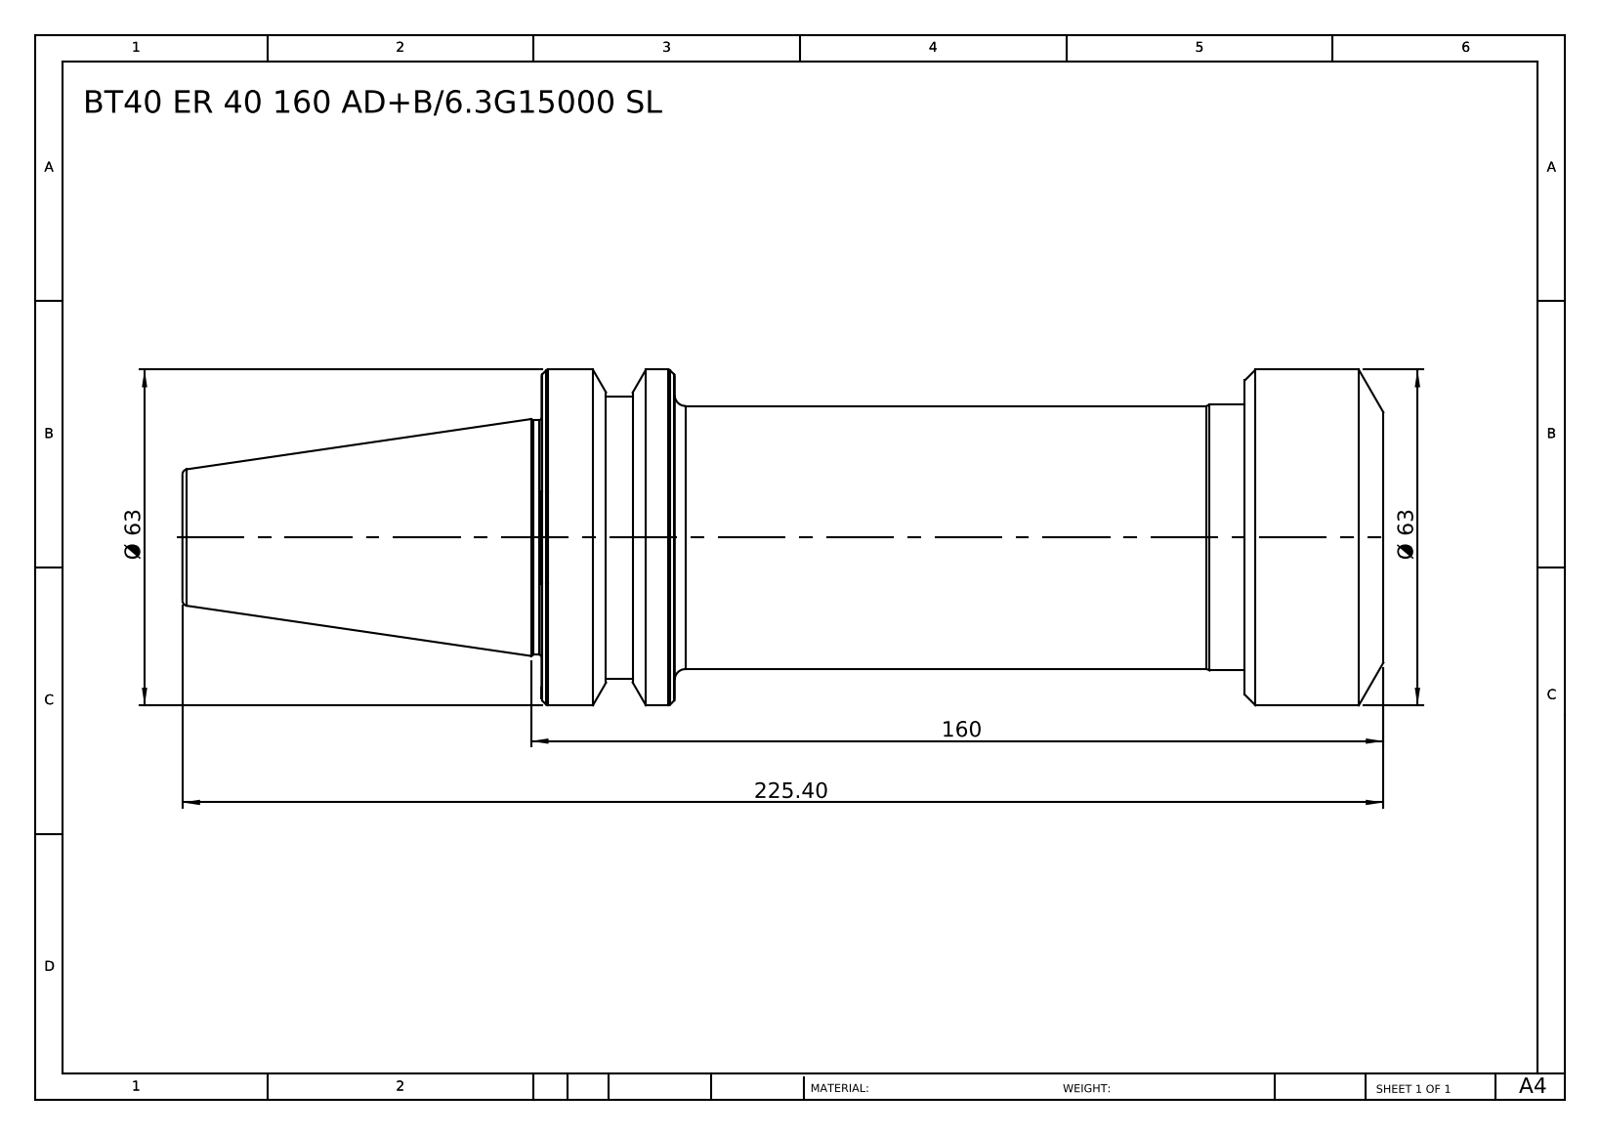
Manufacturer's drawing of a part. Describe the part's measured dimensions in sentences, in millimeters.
The part is named "BT40 ER 40 160 AD-6.3G15000 SL". Its 3-D file was written by "SolidWorks 2014 (CONFIG_CONTROL_DESIGN)". It is 1 solid with 62 faces: 7 planar, 14 cylindrical and 41 other. Overall it measures 225.4 by 63 by 63 millimeters. Its volume is 421 200 cubic millimeters and its surface area 41 394 square millimeters. Round bosses or shafts: 1 of diameter 63, 1 of diameter 53, 1 of diameter 49.9, 1 of diameter 49.4, 1 of diameter 44. The main face-to-face distances are 158, 26, 132, 133, 107, 25, 225.4, 199.4, 92.4, 67.4.
